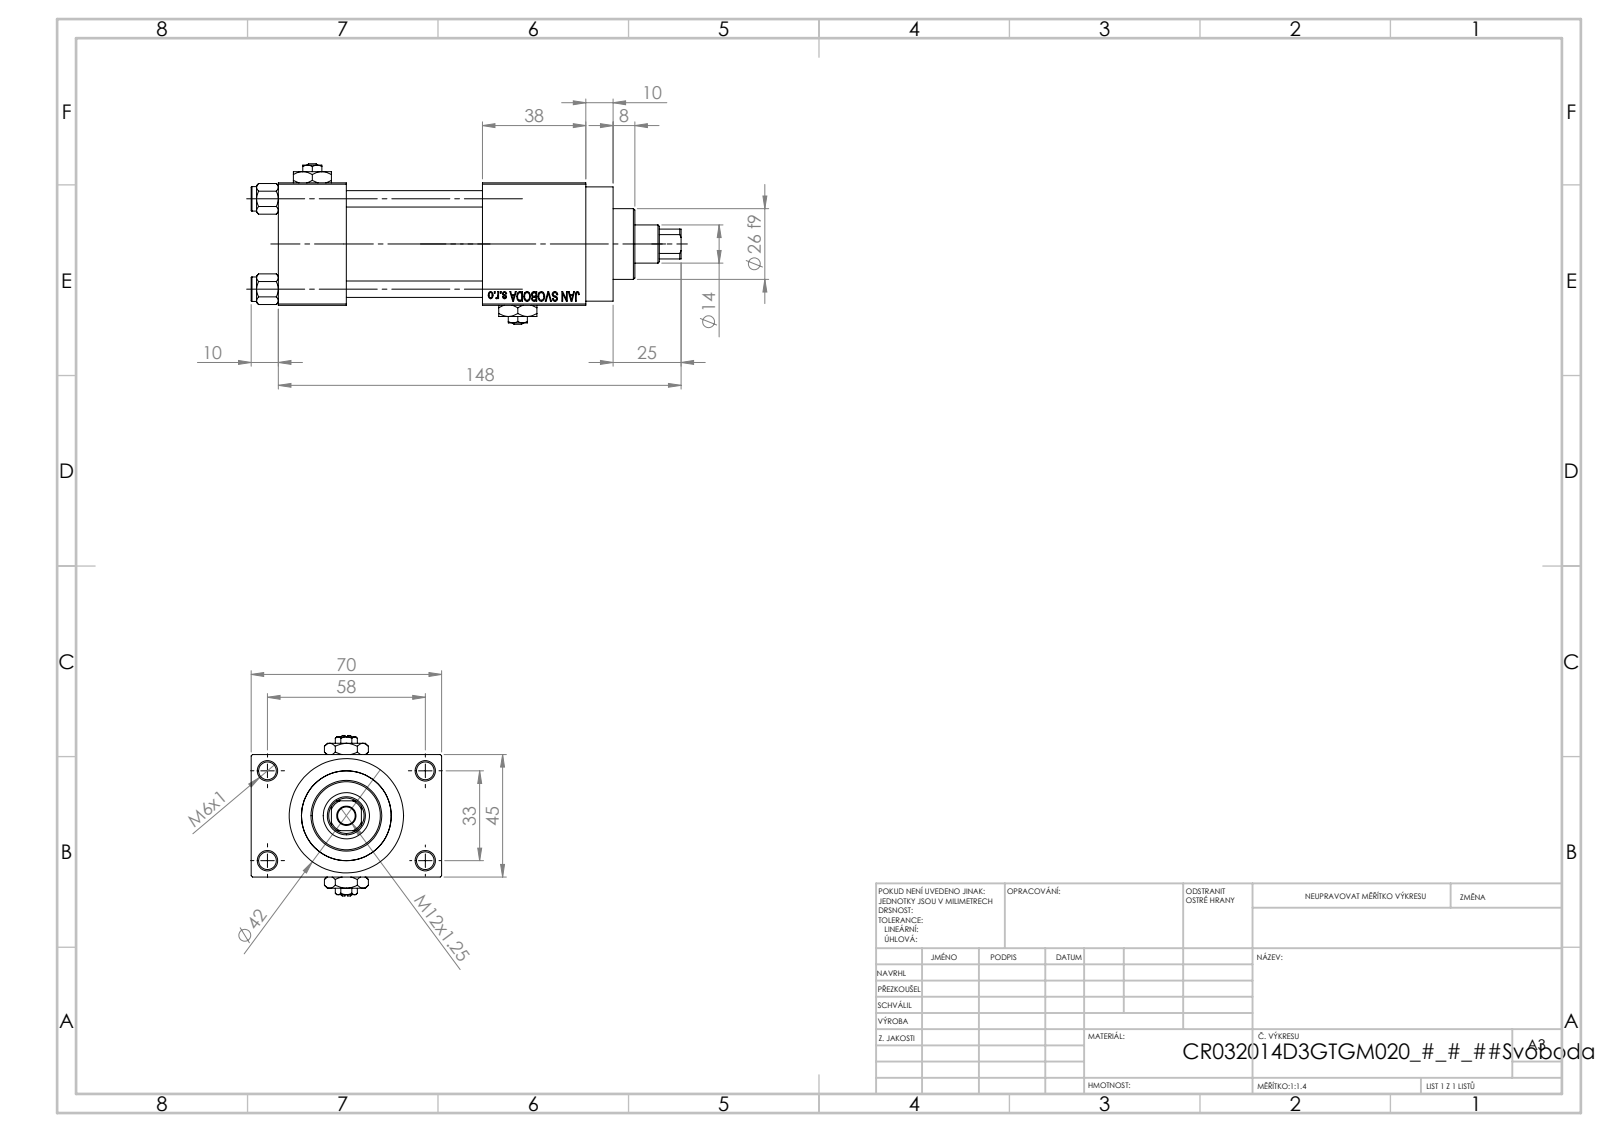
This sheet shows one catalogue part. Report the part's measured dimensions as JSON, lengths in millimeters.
{"part_name": "V215CR_VCP_D; NUT_M5_D; V215_VC_A; V215CR_D_TYCINKA (+2 more)", "step_written_by": "SolidWorks 2019 (CONFIG_CONTROL_DESIGN)", "units": "millimeters", "bodies": {"solids": 13, "faces": 1187, "planar": 540, "cylindrical": 89, "other": 558}, "overall_size": [158, 70, 59], "volume_mm3": 233587, "surface_area_mm2": 76064, "round_holes": [[6.5, 5], [6, 4], [7, 2], [13.16, 2], [20, 2], [14, 1], [17, 1], [24, 1], [32, 1], [33, 1]], "round_bosses_or_shafts": [[9, 4], [42, 1], [38, 1], [26, 1]], "partial_cylinders_radius": [[6.5, 1]], "face_to_face_distances": [45, 25, 12.5, 57.5, 50, 75, 88, 70, 38, 113], "hole_center_spacings": [12.4, 23.48, 33.2, 33.37, 35.35, 45.6, 56.35, 33]}
